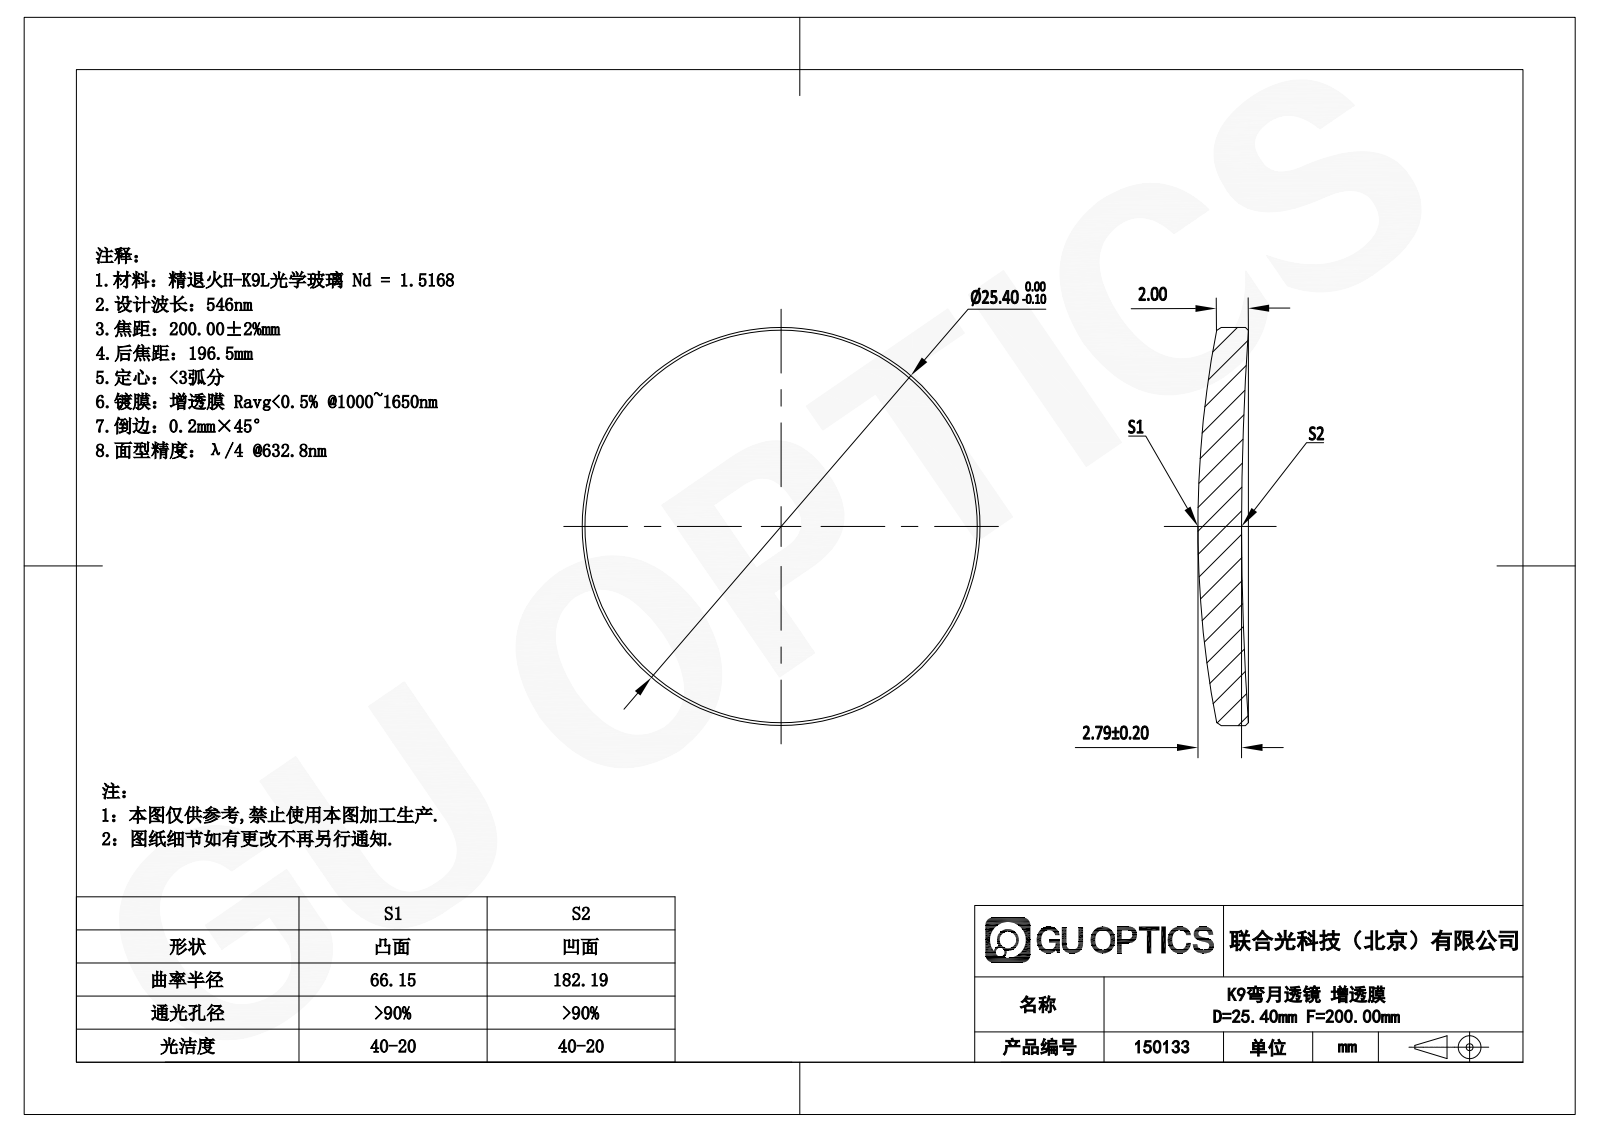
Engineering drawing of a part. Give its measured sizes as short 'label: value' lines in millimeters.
name: GLM1-025B-200-SWIR
written by: SolidWorks 2022 (AUTOMOTIVE_DESIGN)
unit: mm
bodies: 1 solid, 10 faces (0 planar, 2 cylindrical, 8 other)
size: 25.4 × 25.4 × 3.22
volume: 1 210 mm³; area: 1 160 mm²
bosses: 1× ⌀25.4
